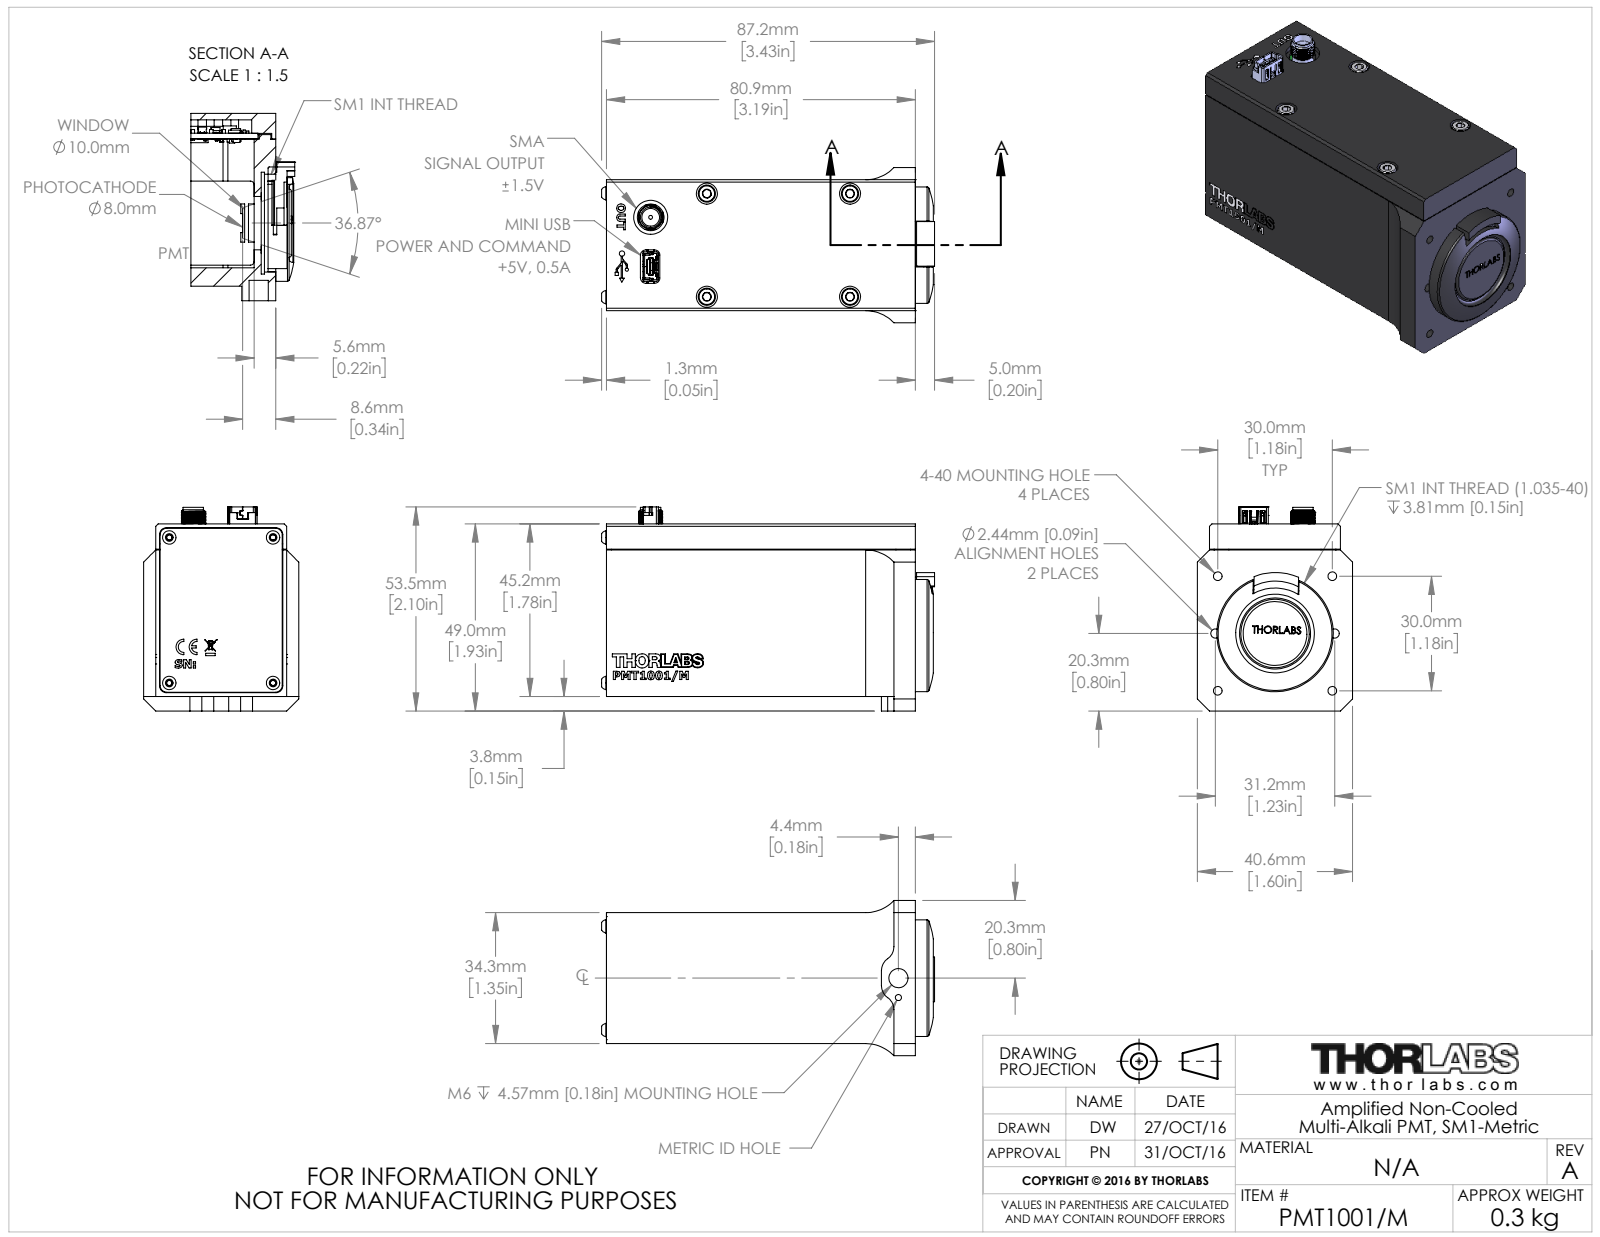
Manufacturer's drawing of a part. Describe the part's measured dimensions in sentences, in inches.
The part is named "TTN117877-E0W". Its 3-D file was written by "SolidWorks 2016 (AUTOMOTIVE_DESIGN)". It is 0 solids with 518 faces: 270 planar, 140 cylindrical and 108 other. Overall it measures 3.433 by 2.105 by 1.6 inches. Round holes: 4 of diameter 0.089, 4 of diameter 0.217, 2 of diameter 0.095, 1 of diameter 0.055, 1 of diameter 0.063, 1 of diameter 0.183, 1 of diameter 0.197, 1 of diameter 0.275, 1 of diameter 0.35, 1 of diameter 0.811. Round bosses or shafts: 4 of diameter 0.177, 4 of diameter 0.138, 1 of diameter 1.201, 1 of diameter 0.246, 1 of diameter 0.211, 1 of diameter 0.013. Partial cylindrical surfaces (rounded edges, fillets, slot ends): 13 of radius 0.004, 9 of radius 0.02, 8 of radius 0.07, 4 of radius 0.055, 4 of radius 0.15, 3 of radius 0.006, 3 of radius 0.012, 2 of radius 0.006. The main face-to-face distances are 1.35, 1.78, 1.577, 0.203, 3.185, 0.118, 3.303, 1.511, 0.066, 0.269. The hole center spacings are 0.591, 0.835, 1.181, 0.729, 1.063, 1.343, 1.343, 1.476.
